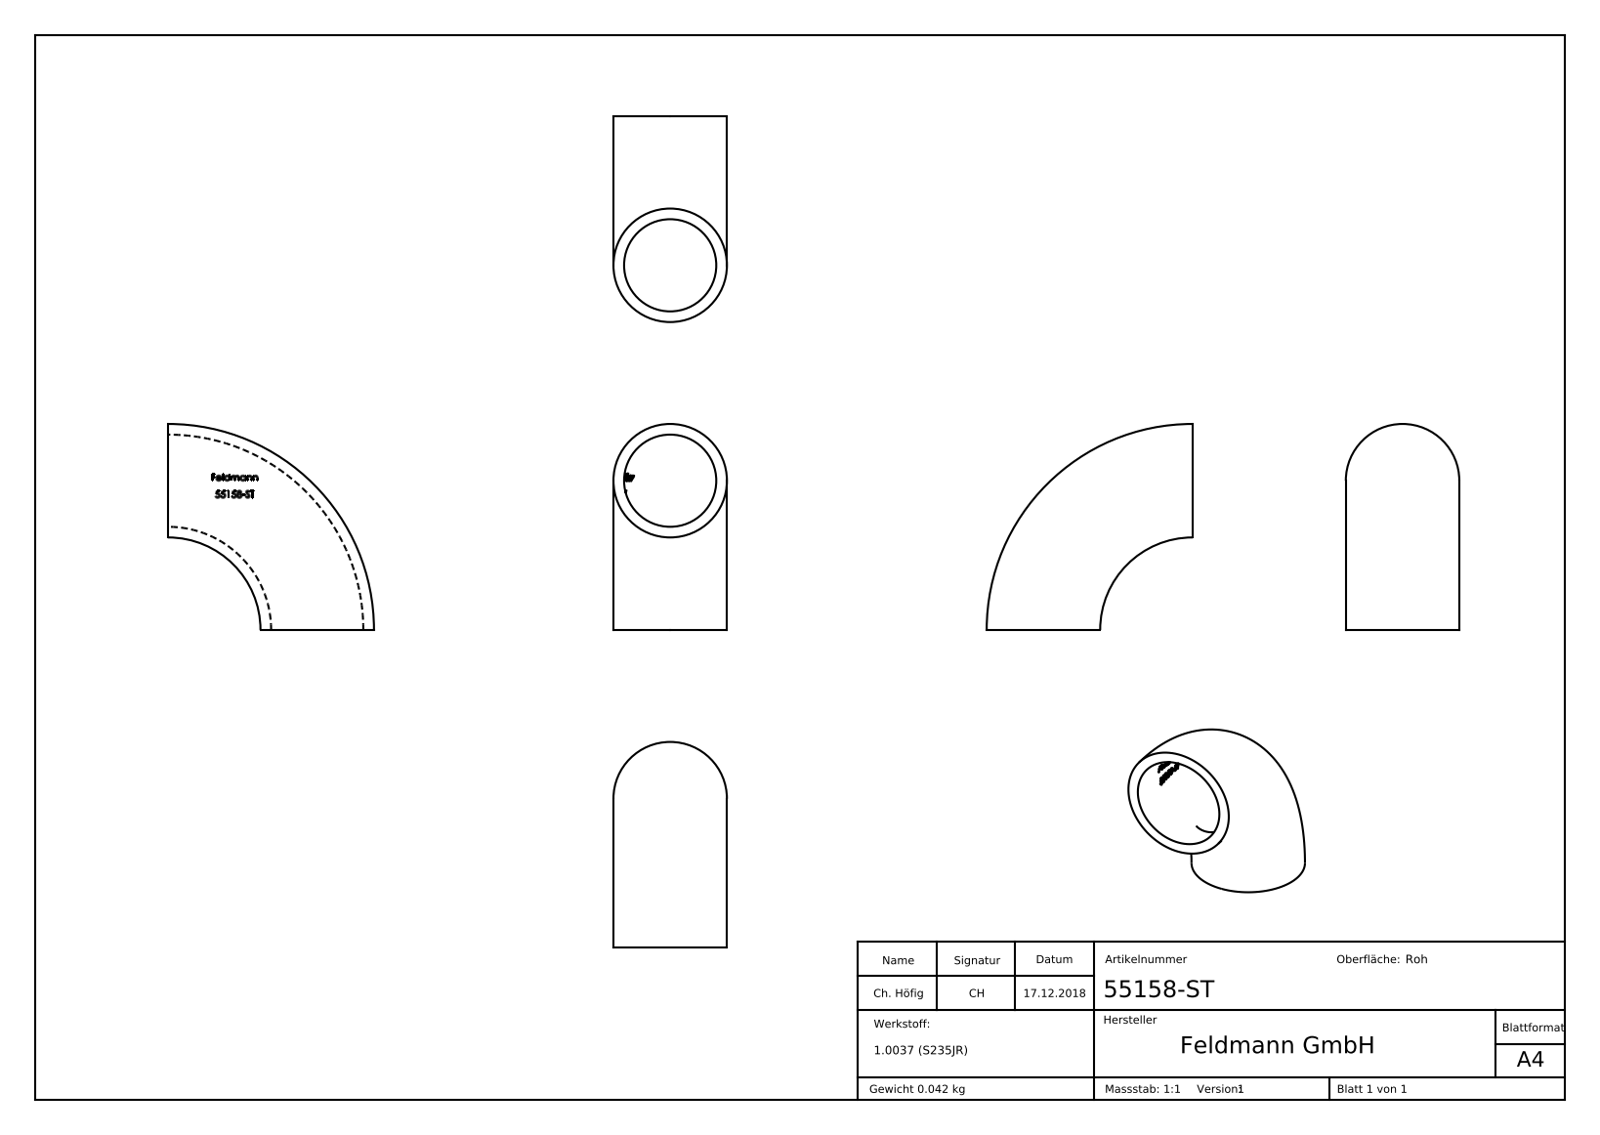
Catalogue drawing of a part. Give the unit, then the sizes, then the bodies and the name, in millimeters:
Units: millimetres
Overall size (bounding box): 38.65 × 38.65 × 21.3
Main face-to-face distances: 3.09, 2.97, 3.27, 0.39, 3.54, 1.12, 2.02, 26.12, 3.66, 4.43
Volume: 5 333 mm³ · Surface area: 5 585 mm²
Bodies: 1 solid, 223 faces (94 planar, 0 cylindrical, 129 other)
Part name (STEP PRODUCT): 55158-ST
STEP written by: SolidWorks 2015 (CONFIG_CONTROL_DESIGN)
